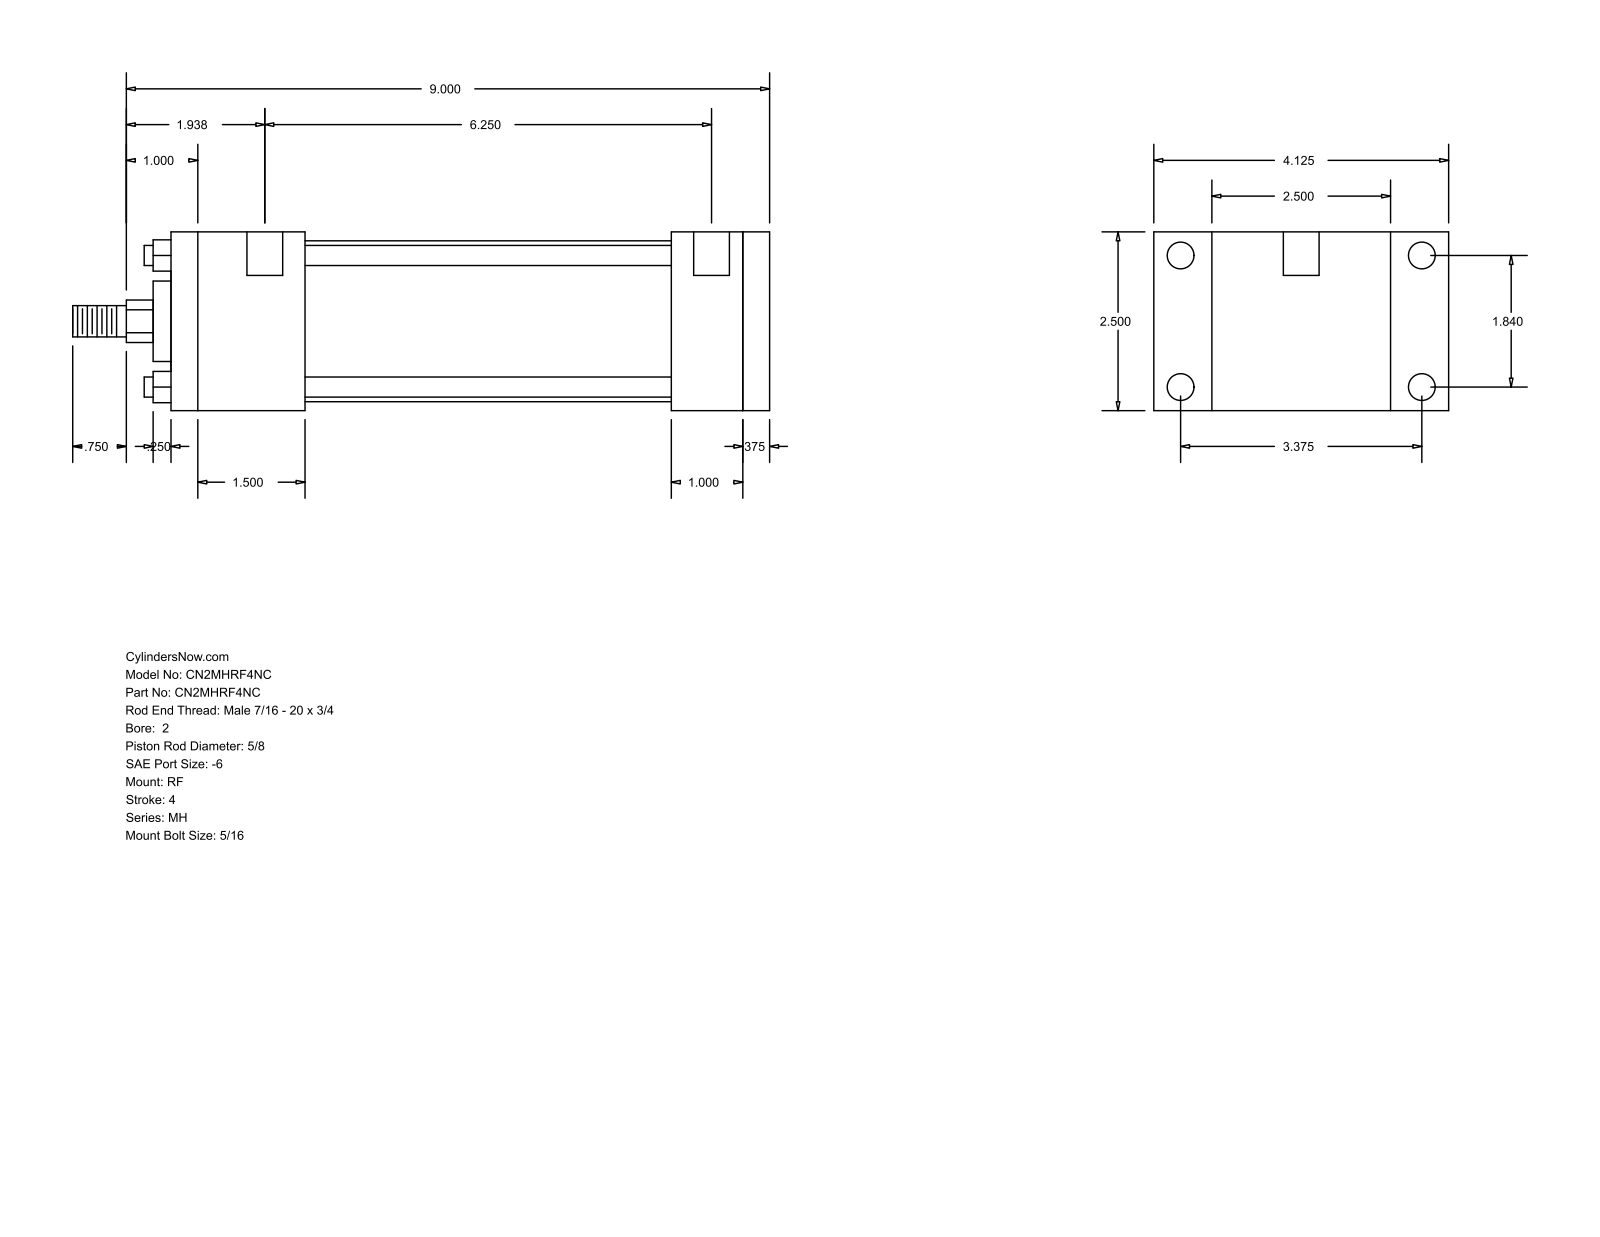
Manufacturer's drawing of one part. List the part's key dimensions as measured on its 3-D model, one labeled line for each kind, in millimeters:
Part name (STEP PRODUCT): MH_RF__0200_0.625
STEP written by: GSSL Pune (CONFIG_CONTROL_DESIGN)
Units: millimetres
Bodies: 0 solids, 92 faces (64 planar, 28 cylindrical, 0 other)
Overall size (bounding box): 247.65 × 104.78 × 63.5
Round holes (diameter × count): ⌀5.56 ×4, ⌀9.53 ×4, ⌀12.7 ×2
Round bosses / shafts (diameter × count): ⌀7.14 ×4, ⌀57.15 ×1, ⌀28.57 ×1, ⌀15.88 ×1, ⌀11.11 ×1
Partial cylindrical surfaces — rounded edges, fillets, slot ends (radius × count): R7.54 ×1
Main face-to-face distances: 63.5, 212.72, 9.53, 203.19, 47.62, 177.8, 130.18, 155.57, 165.1, 25.39
Hole centre spacings: 46.74, 85.72, 97.63, 166.69, 3.18, 4.76, 158.75, 161.93
